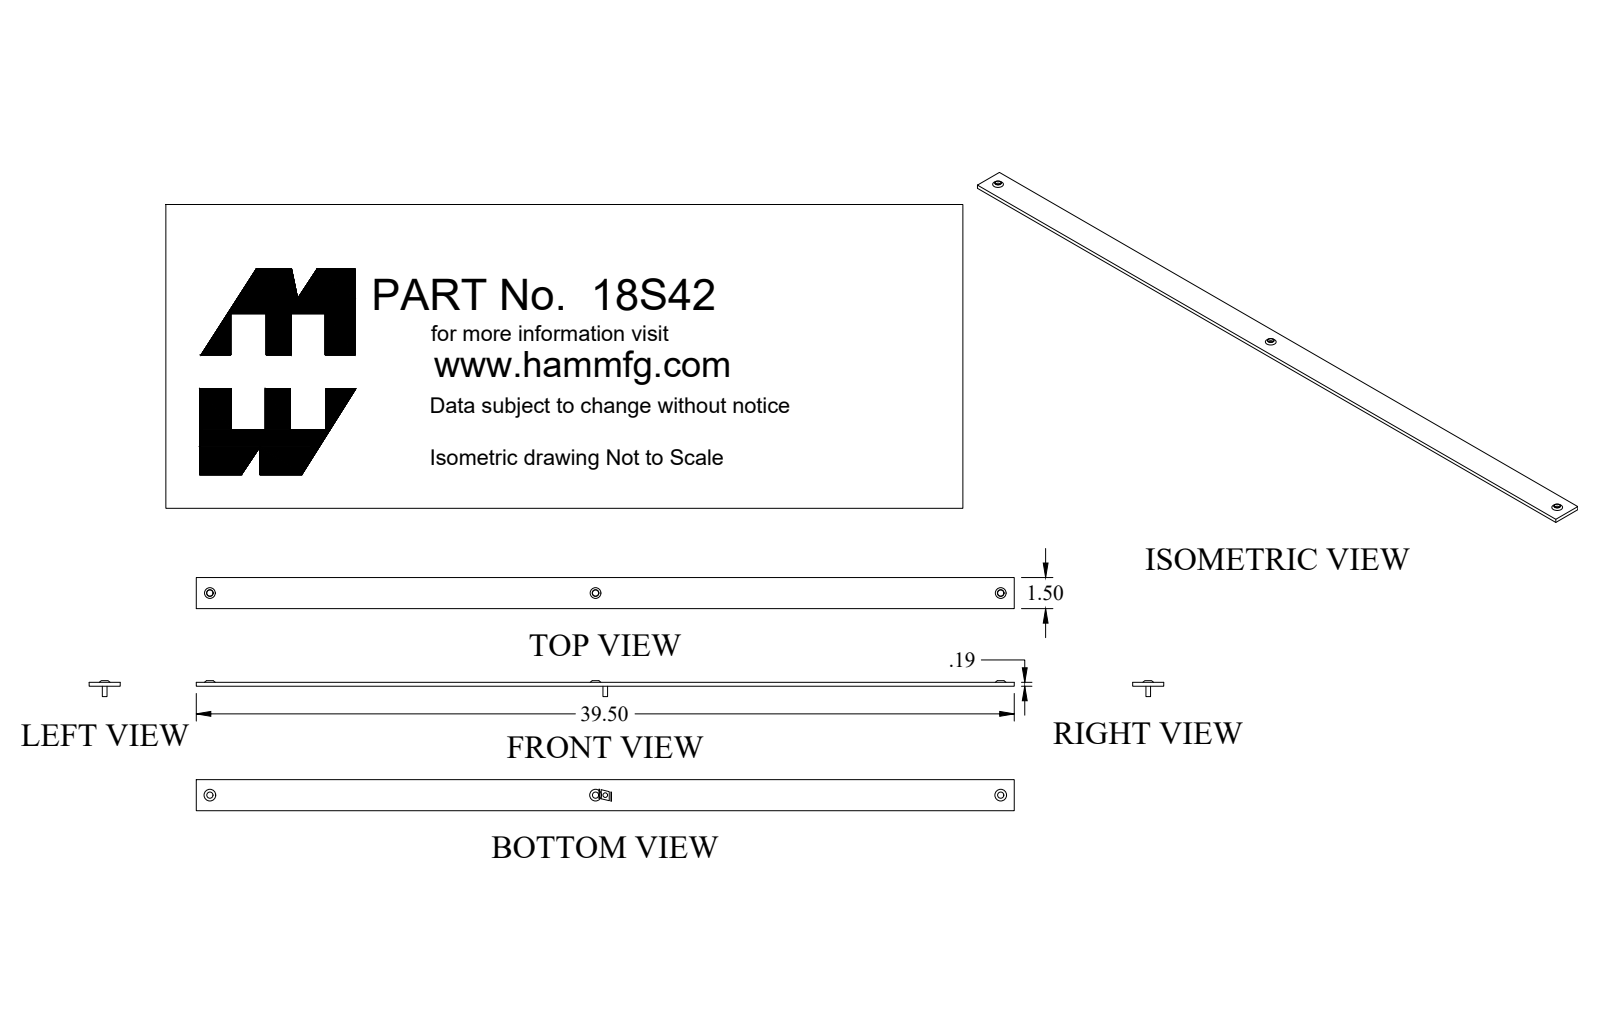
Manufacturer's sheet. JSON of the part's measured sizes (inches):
{"part_name": "18S42_Default", "step_written_by": "SolidWorks 2018 (CONFIG_CONTROL_DESIGN)", "units": "inches", "bodies": {"solids": 1, "faces": 27, "planar": 9, "cylindrical": 6, "other": 12}, "overall_size": [39.5, 1.5, 0.27], "volume_in3": 11.08, "surface_area_in2": 134.2, "round_holes": [[0.296, 3]], "face_to_face_distances": [0.188, 1.5, 39.5, 0.27, 0.082], "hole_center_spacings": [18.625, 19.563, 38.188]}
